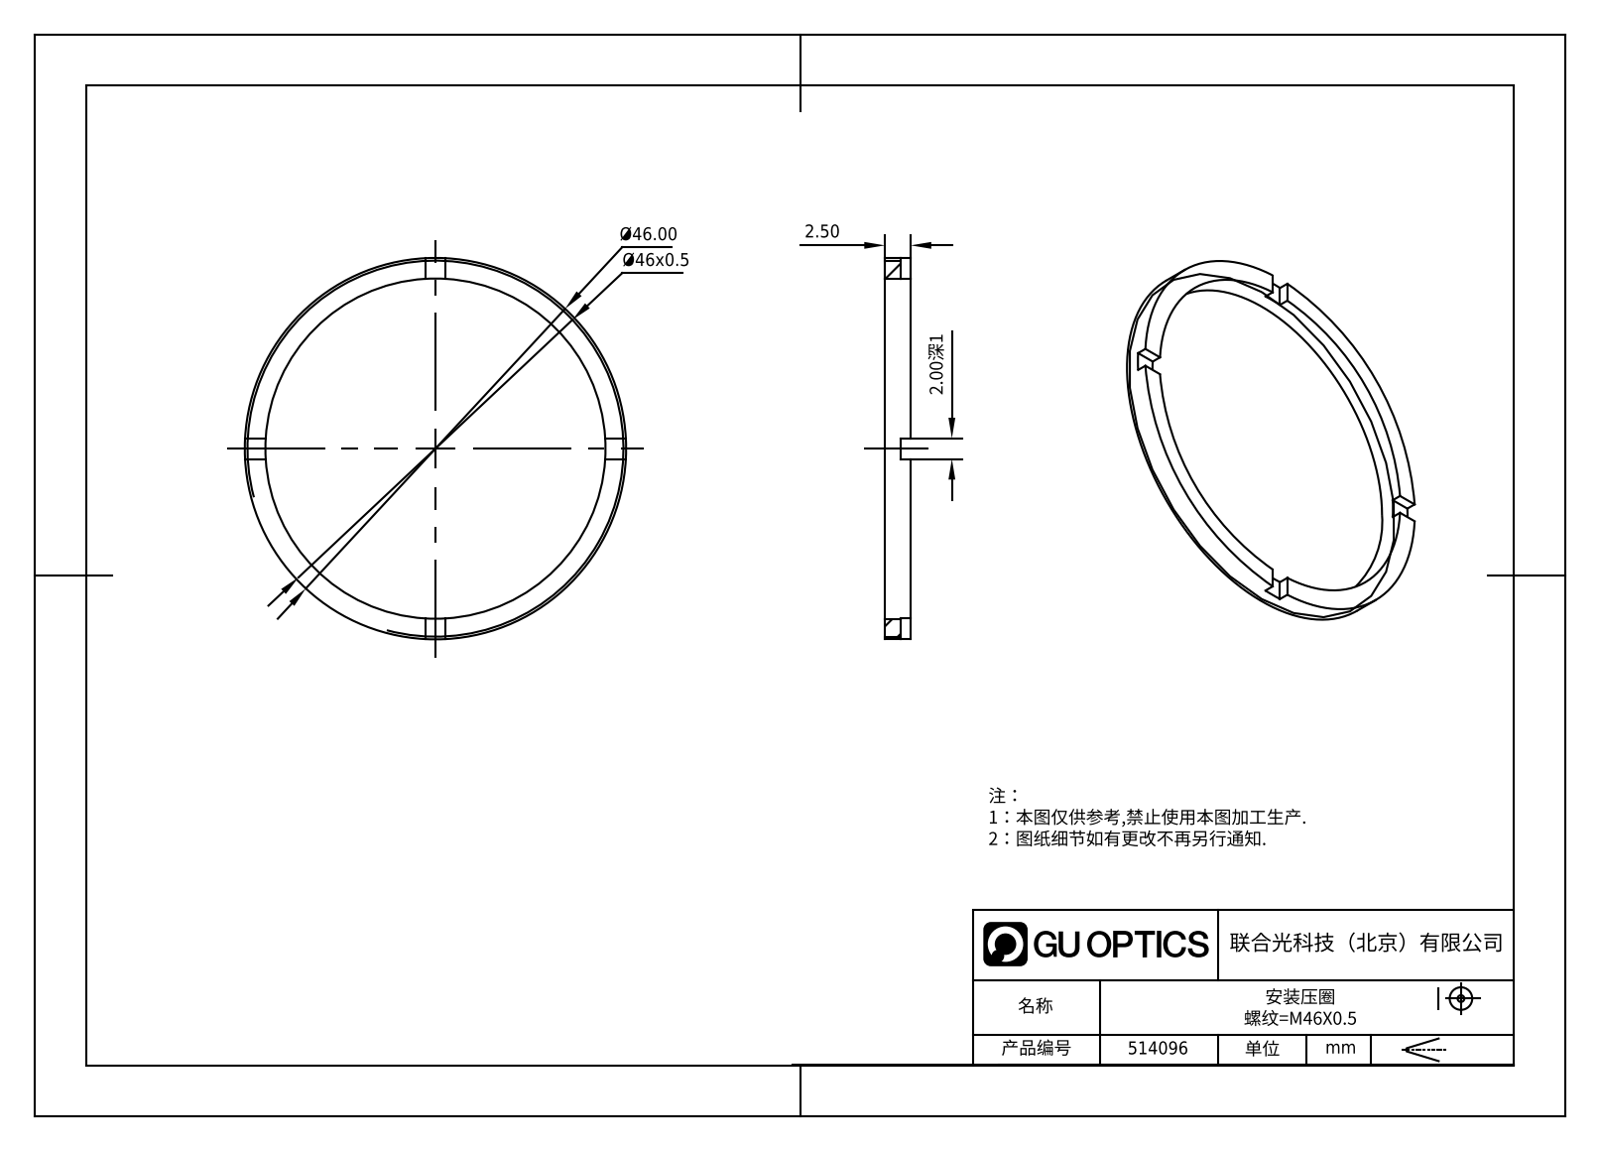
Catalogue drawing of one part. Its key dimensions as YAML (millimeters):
part_name: "514096"
step_written_by: "SolidWorks 2020 (CONFIG_CONTROL_DESIGN)"
units: millimeters
bodies: {solids: 1, faces: 21, planar: 17, cylindrical: 4, other: 0}
overall_size: [46, 46, 2.5]
volume: 675
surface_area: 1244
round_holes:
  - {diameter: 42, count: 1}
round_bosses_or_shafts:
  - {diameter: 46, count: 1}
face_to_face_distances: [2.5, 1.5, 1, 2]
